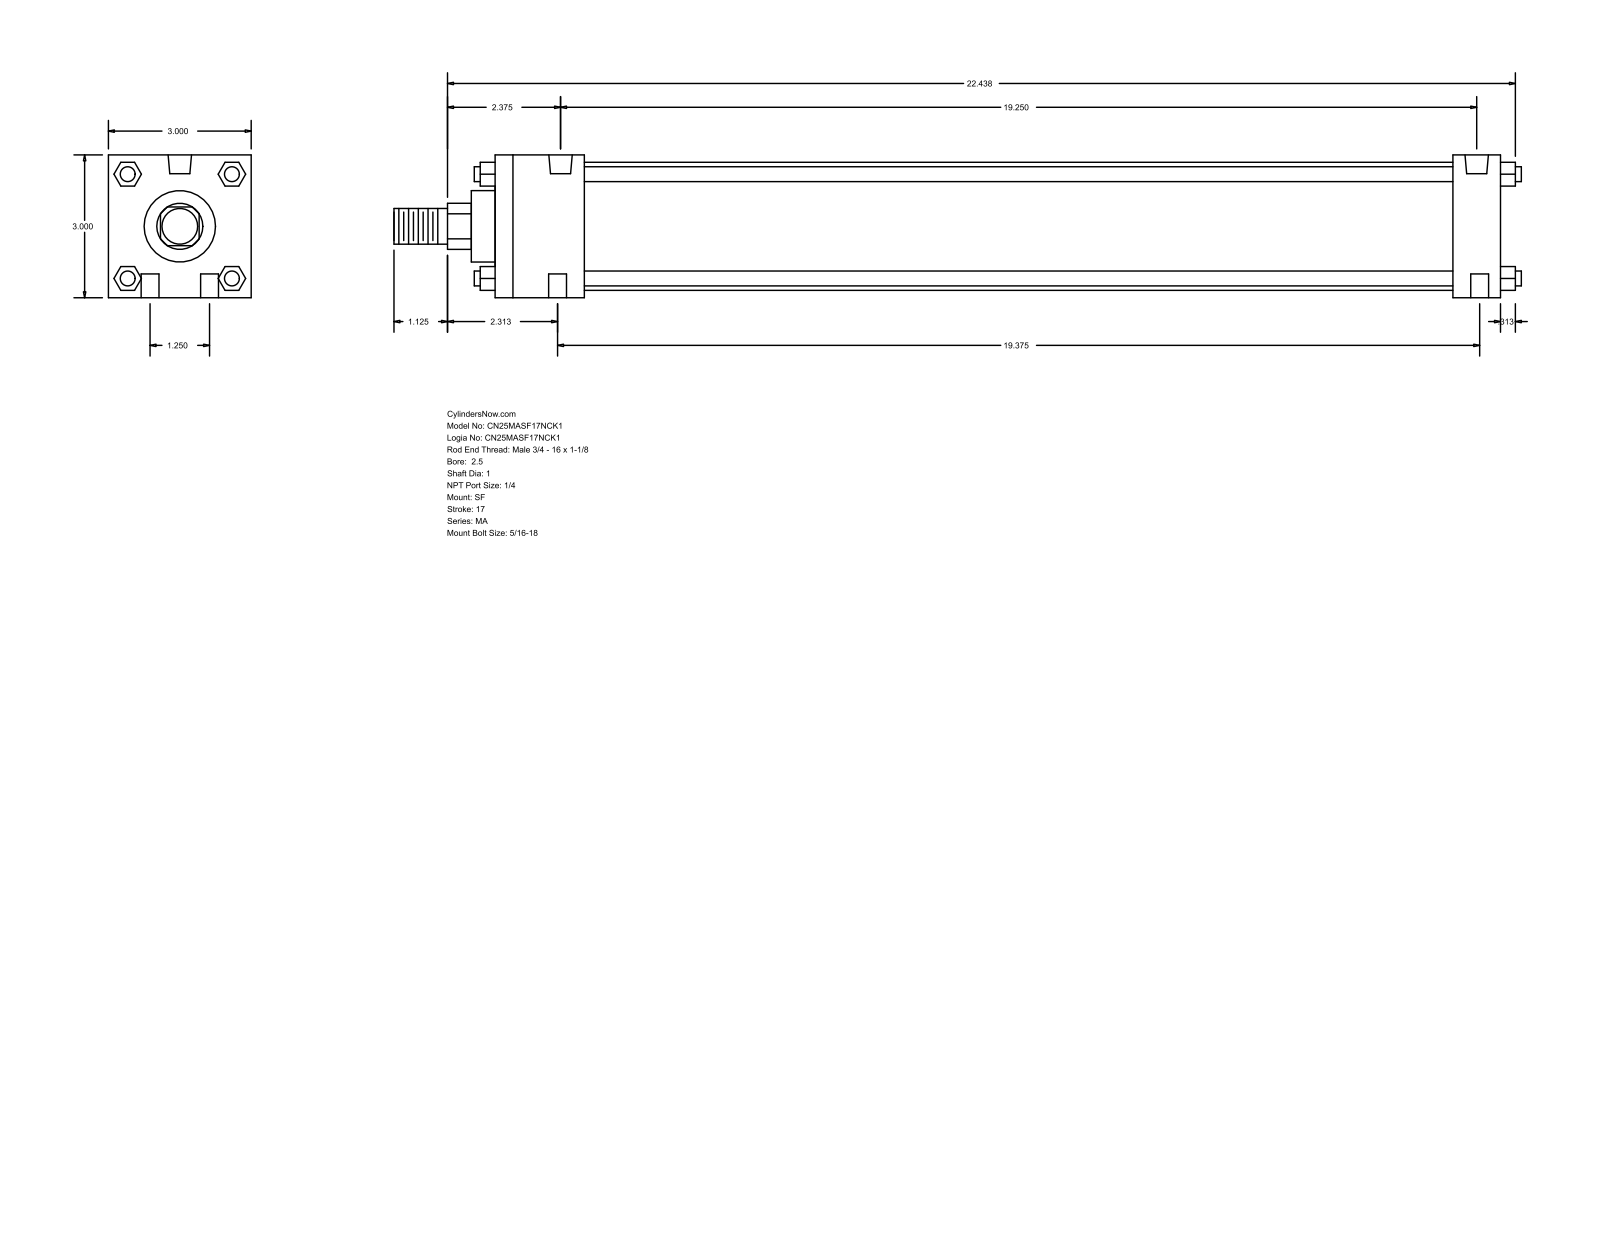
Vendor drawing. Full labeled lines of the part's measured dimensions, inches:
Part name (STEP PRODUCT): MA_SF__0250_1
STEP written by: GSSL Pune (CONFIG_CONTROL_DESIGN)
Units: inches
Bodies: 0 solids, 124 faces (94 planar, 30 cylindrical, 0 other)
Overall size (bounding box): 23.687 × 3 × 3
Round holes (diameter × count): ⌀0.375 ×4, ⌀0.313 ×2, ⌀0.492 ×2
Round bosses / shafts (diameter × count): ⌀0.313 ×4, ⌀2.69 ×1, ⌀1.5 ×1, ⌀1 ×1, ⌀0.75 ×1
Partial cylindrical surfaces — rounded edges, fillets, slot ends (radius × count): R0.484 ×1
Main face-to-face distances: 3, 21.125, 0.5, 1, 20.125, 1.875, 18.25, 19.25, 1.095, 1.896
Hole centre spacings: 0.628, 19.322, 1.25, 19.25, 19.375, 19.415
